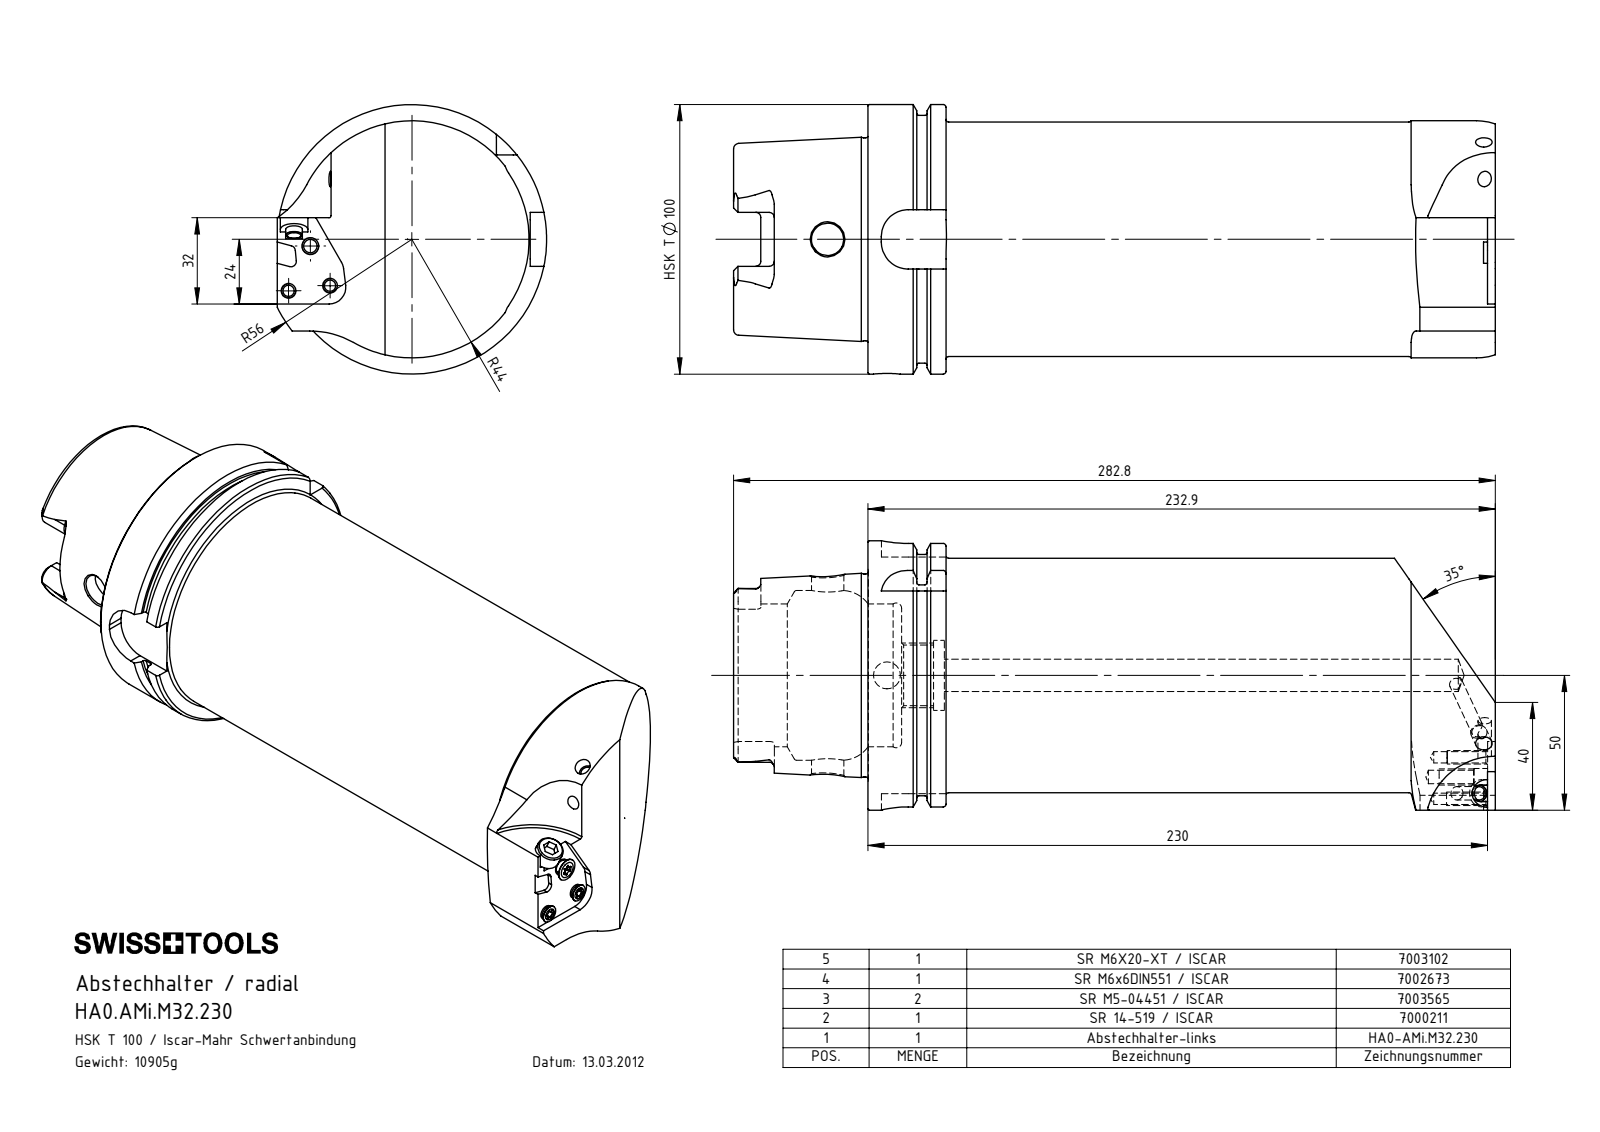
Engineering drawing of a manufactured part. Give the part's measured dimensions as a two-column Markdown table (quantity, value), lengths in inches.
| quantity | value |
| --- | --- |
| part name | HA0-AMi.M32.110_A_L230; SR M6X6DIN551; HA0.AMi.M32.230; SR M5-04451 (+3 more) |
| STEP written by | SolidWorks 2017 (AUTOMOTIVE_DESIGN) |
| units | inches |
| bodies | 8 solids, 308 faces (102 planar, 112 cylindrical, 94 other) |
| overall size | 11.209 × 3.937 × 3.937 |
| volume | 85.25 in³ |
| surface area | 178.8 in² |
| round holes (diameter × count) | 0.197 × 4, 0.165 × 2, 0.472 × 2, 0.248 × 1, 0.394 × 1, 0.886 × 1, 1.024 × 1, 2.087 × 1, 2.48 × 1 |
| round bosses / shafts (diameter × count) | 0.236 × 4, 0.256 × 2, 0.197 × 2, 3.937 × 1, 3.62 × 1, 3.425 × 1, 2.963 × 1, 0.394 × 1 |
| partial cylindrical surfaces (radius × count) | 0.039 × 20, 0.075 × 6, 0.394 × 4, 0.078 × 3, 0.079 × 2, 0.19 × 2, 0.192 × 2, 0.244 × 2 |
| main face-to-face distances | 9.169, 0.49, 8.679, 1.14, 0.65, 8.03, 1.965, 2.455, 3.104, 11.134 |
| hole center spacings | 0.611, 0.646, 0.727, 1.375, 1.487, 1.954 |
